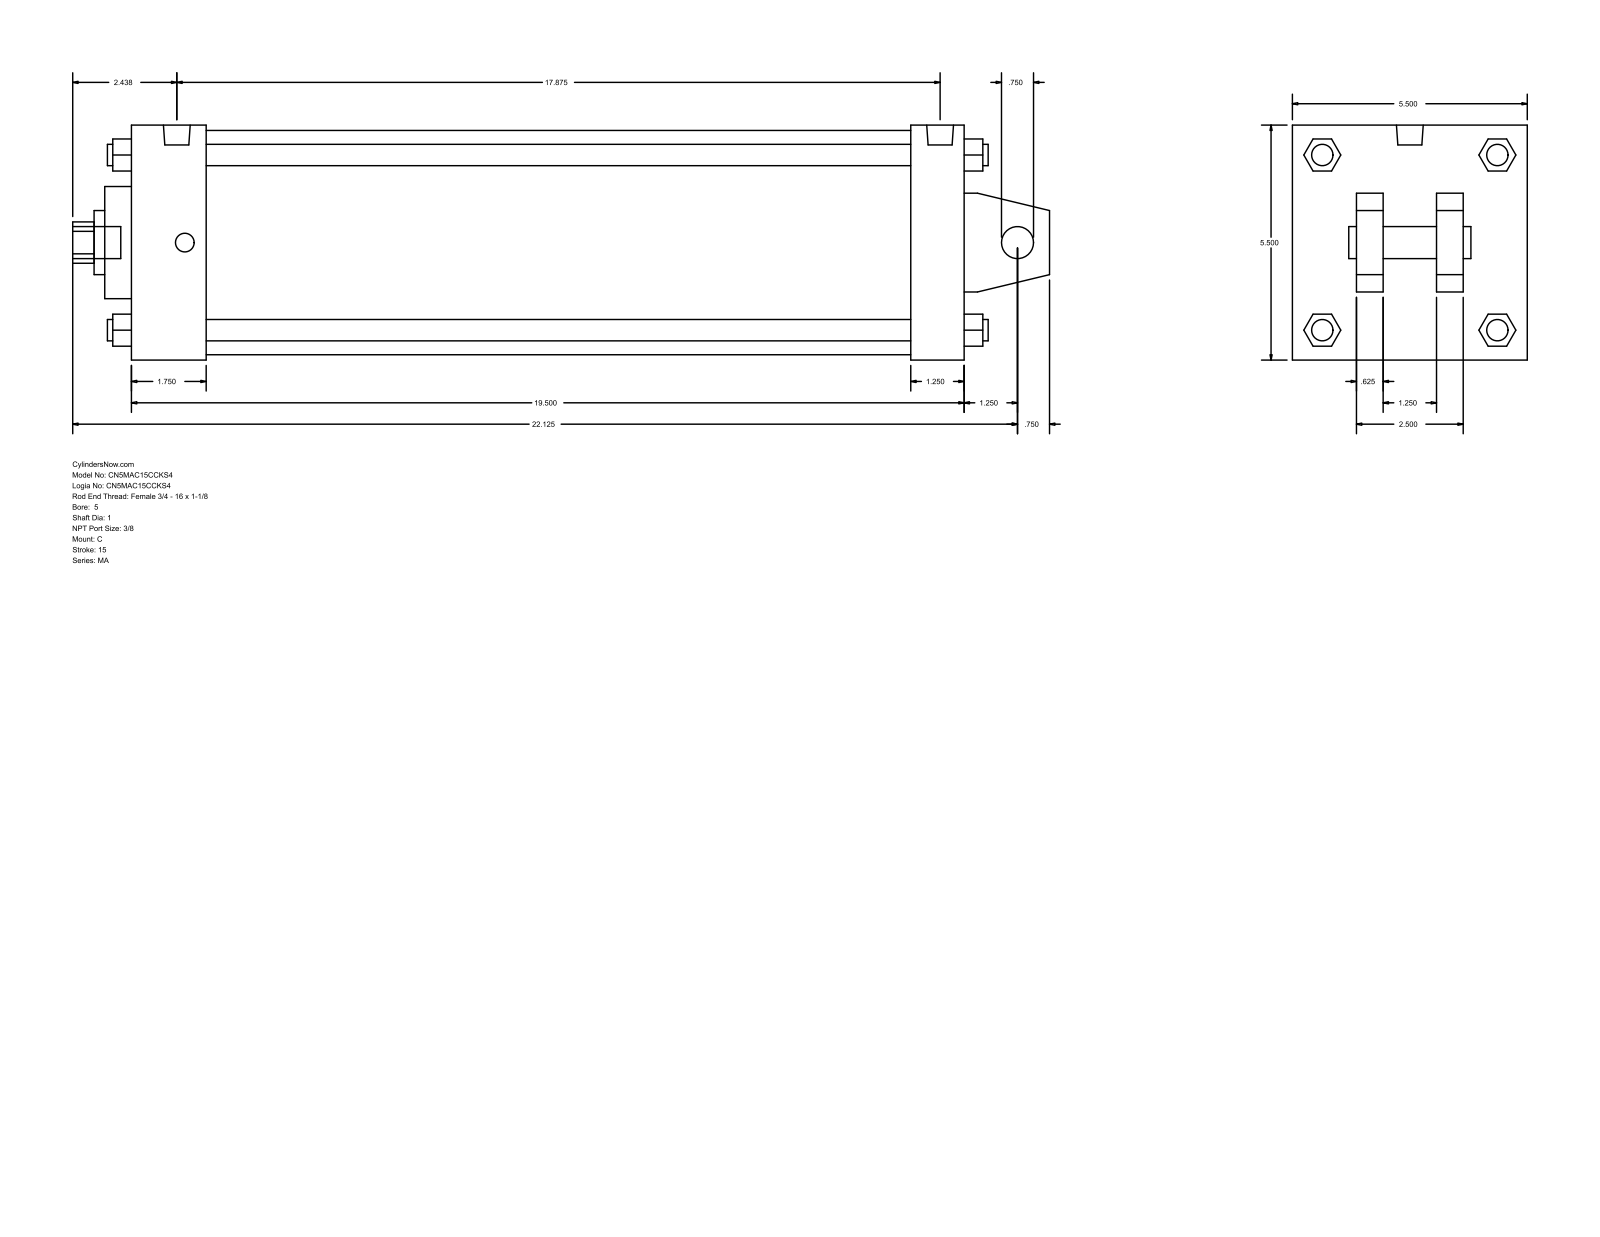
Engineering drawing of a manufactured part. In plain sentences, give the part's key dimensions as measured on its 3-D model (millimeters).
The part is named "MA_C__0500_1". Its 3-D file was written by "GSSL Pune (CONFIG_CONTROL_DESIGN)". It is 0 solids with 141 faces: 109 planar, 32 cylindrical and 0 other. Overall it measures 581.02 by 139.7 by 139.7 millimeters. Round holes: 1 of diameter 19.05, 1 of diameter 25.4, 1 of diameter 38.1, 1 of diameter 66.67, 1 of diameter 133.35. Round bosses or shafts: 4 of diameter 12.7, 4 of diameter 11.11, 2 of diameter 15.93, 1 of diameter 19.05. Partial cylindrical surfaces (rounded edges, fillets, slot ends): 1 of radius 12.29. The main face-to-face distances are 139.7, 495.31, 15.87, 463.56, 31.75, 44.46, 419.1, 450.85, 38.1, 101.6.
